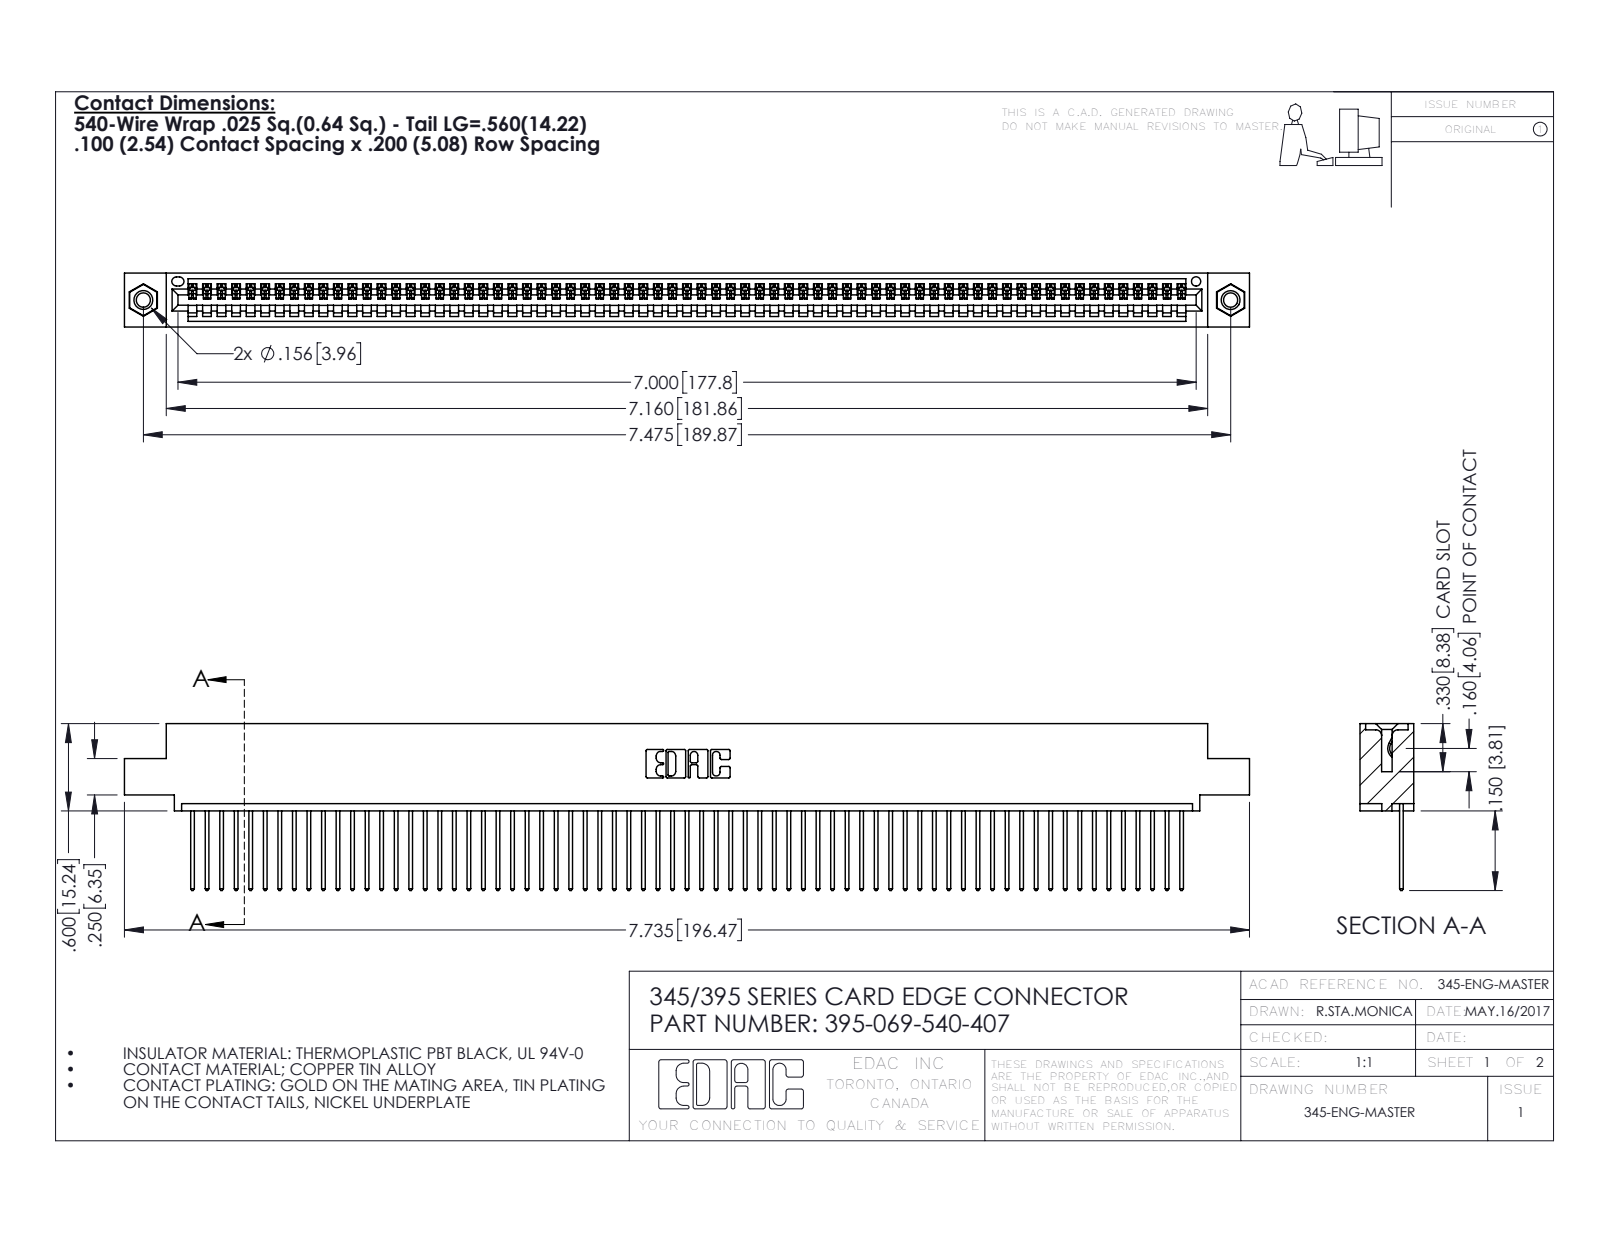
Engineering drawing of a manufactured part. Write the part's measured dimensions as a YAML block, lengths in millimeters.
part_name: "395-069-540-407; 345 Part_0.110 Offset - 0.156 Dia-TI; 345-250-001_345-250-005-103; 345-292-001_345-293-140"
step_written_by: "SolidWorks 2016 (CONFIG_CONTROL_DESIGN)"
units: millimeters
bodies: {solids: 72, faces: 4192, planar: 2876, cylindrical: 1300, other: 16}
overall_size: [196.5, 29.1, 9.4]
volume: 18890
surface_area: 26260
round_holes:
  - {diameter: 2.5, count: 2}
  - {diameter: 3.2, count: 2}
  - {diameter: 4, count: 2}
  - {diameter: 1.6, count: 1}
round_bosses_or_shafts:
  - {diameter: 3.9, count: 2}
partial_cylinders:
  - {radius: 0.2, count: 138}
  - {radius: 0.3, count: 138}
  - {radius: 0.3, count: 22}
  - {radius: 0.2, count: 6}
  - {radius: 0.8, count: 6}
  - {radius: 0.7, count: 3}
  - {radius: 0.8, count: 2}
  - {radius: 1, count: 2}
face_to_face_distances: [1.8, 7.6, 9.4, 2.5, 6.9, 0.6, 5.1, 5.7, 3.8, 1.8]
hole_center_spacings: [6.9, 183.9, 189.9]
